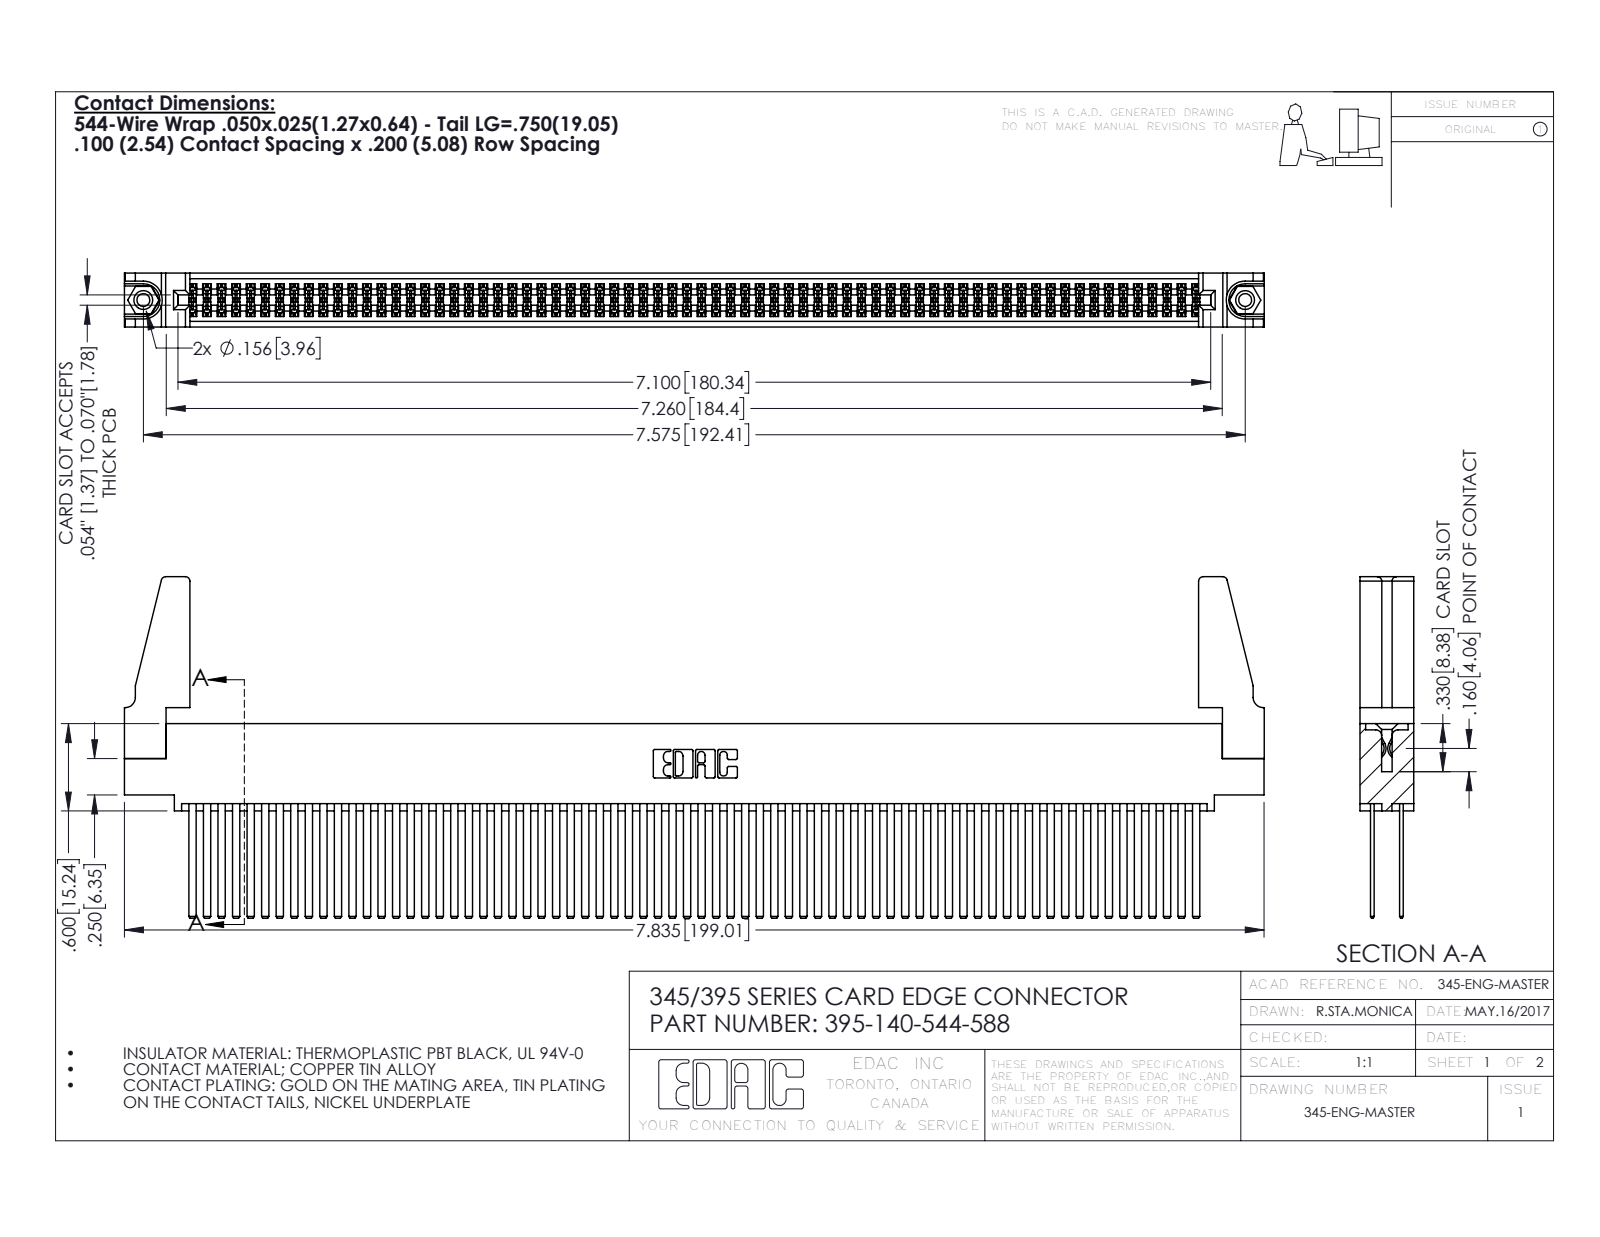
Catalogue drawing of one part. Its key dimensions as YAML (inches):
part_name: "345-292-001_345-293-144; 345 Part_0.110 Offset - 0.156 Dia-TH; 395-140-544-588; 345-250-001_345-250-001-102 (+1 more)"
step_written_by: "SolidWorks 2016 (CONFIG_CONTROL_DESIGN)"
units: inches
bodies: {solids: 145, faces: 6414, planar: 4216, cylindrical: 2182, other: 16}
overall_size: [7.836, 2.347, 0.37]
volume: 1.509
surface_area: 63.96
round_holes:
  - {diameter: 0.089, count: 2}
  - {diameter: 0.125, count: 2}
  - {diameter: 0.156, count: 2}
  - {diameter: 0.064, count: 1}
round_bosses_or_shafts:
  - {diameter: 0.155, count: 2}
partial_cylinders:
  - {radius: 0.006, count: 210}
  - {radius: 0.01, count: 22}
  - {radius: 0.03, count: 8}
  - {radius: 0.007, count: 6}
  - {radius: 0.031, count: 6}
  - {radius: 0.026, count: 3}
  - {radius: 0.014, count: 2}
  - {radius: 0.019, count: 2}
face_to_face_distances: [0.072, 0.298, 0.2, 0.098, 0.272, 0.025, 0.225, 0.37, 0.175, 0.149]
hole_center_spacings: [0.27, 7.339, 7.575]
